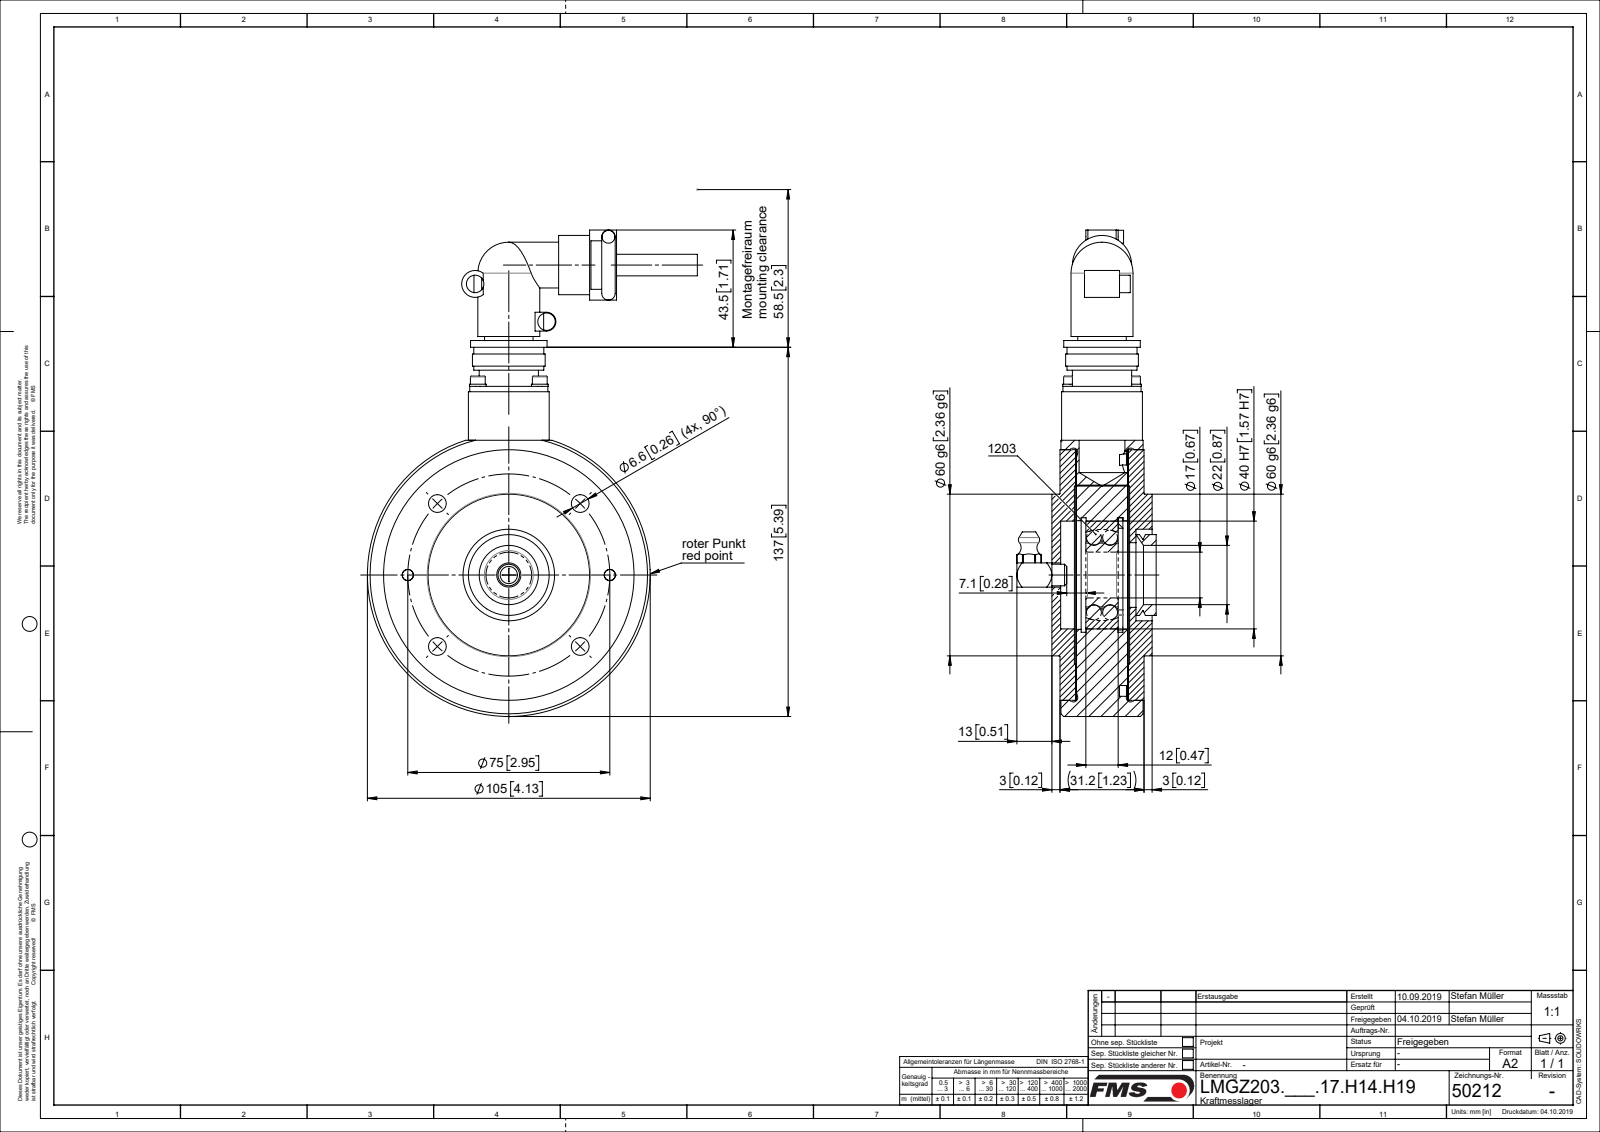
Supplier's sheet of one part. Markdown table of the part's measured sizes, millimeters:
| quantity | value |
| --- | --- |
| part name | ZEICHNUNG7; L50212; L4795904; L47958(1) (+8 more) |
| STEP written by | Mechanical Desktop 2007 (CONFIG_CONTROL_DESIGN) |
| units | millimeters |
| bodies | 21 solids, 415 faces (133 planar, 229 cylindrical, 53 other) |
| overall size | 180.5 × 122.5 × 51.7 |
| volume | 297 689 mm³ |
| surface area | 106 761 mm² |
| round holes (diameter × count) | 2.6 × 4, 3.2 × 4, 3.4 × 4, 3.5 × 4, 6.6 × 4, 4 × 2, 5.3 × 2, 5.5 × 2, 10 × 2, 8.68 × 1, 17 × 1, 22 × 1 |
| round bosses / shafts (diameter × count) | 8 × 4, 6.2 × 4, 5.5 × 4, 3 × 4, 22 × 2, 6.5 × 2, 5 × 2, 4.8 × 2 |
| partial cylindrical surfaces (radius × count) | 2.5 × 2, 2 × 1, 3.5 × 1, 5 × 1 |
| main face-to-face distances | 19.25, 19, 5.85, 25.1, 6.1, 25.35, 19.5, 20, 3, 0.5 |
| hole center spacings | 37.5, 16.26, 23, 28.7, 53.04, 69.3, 32.53, 75.01 |
